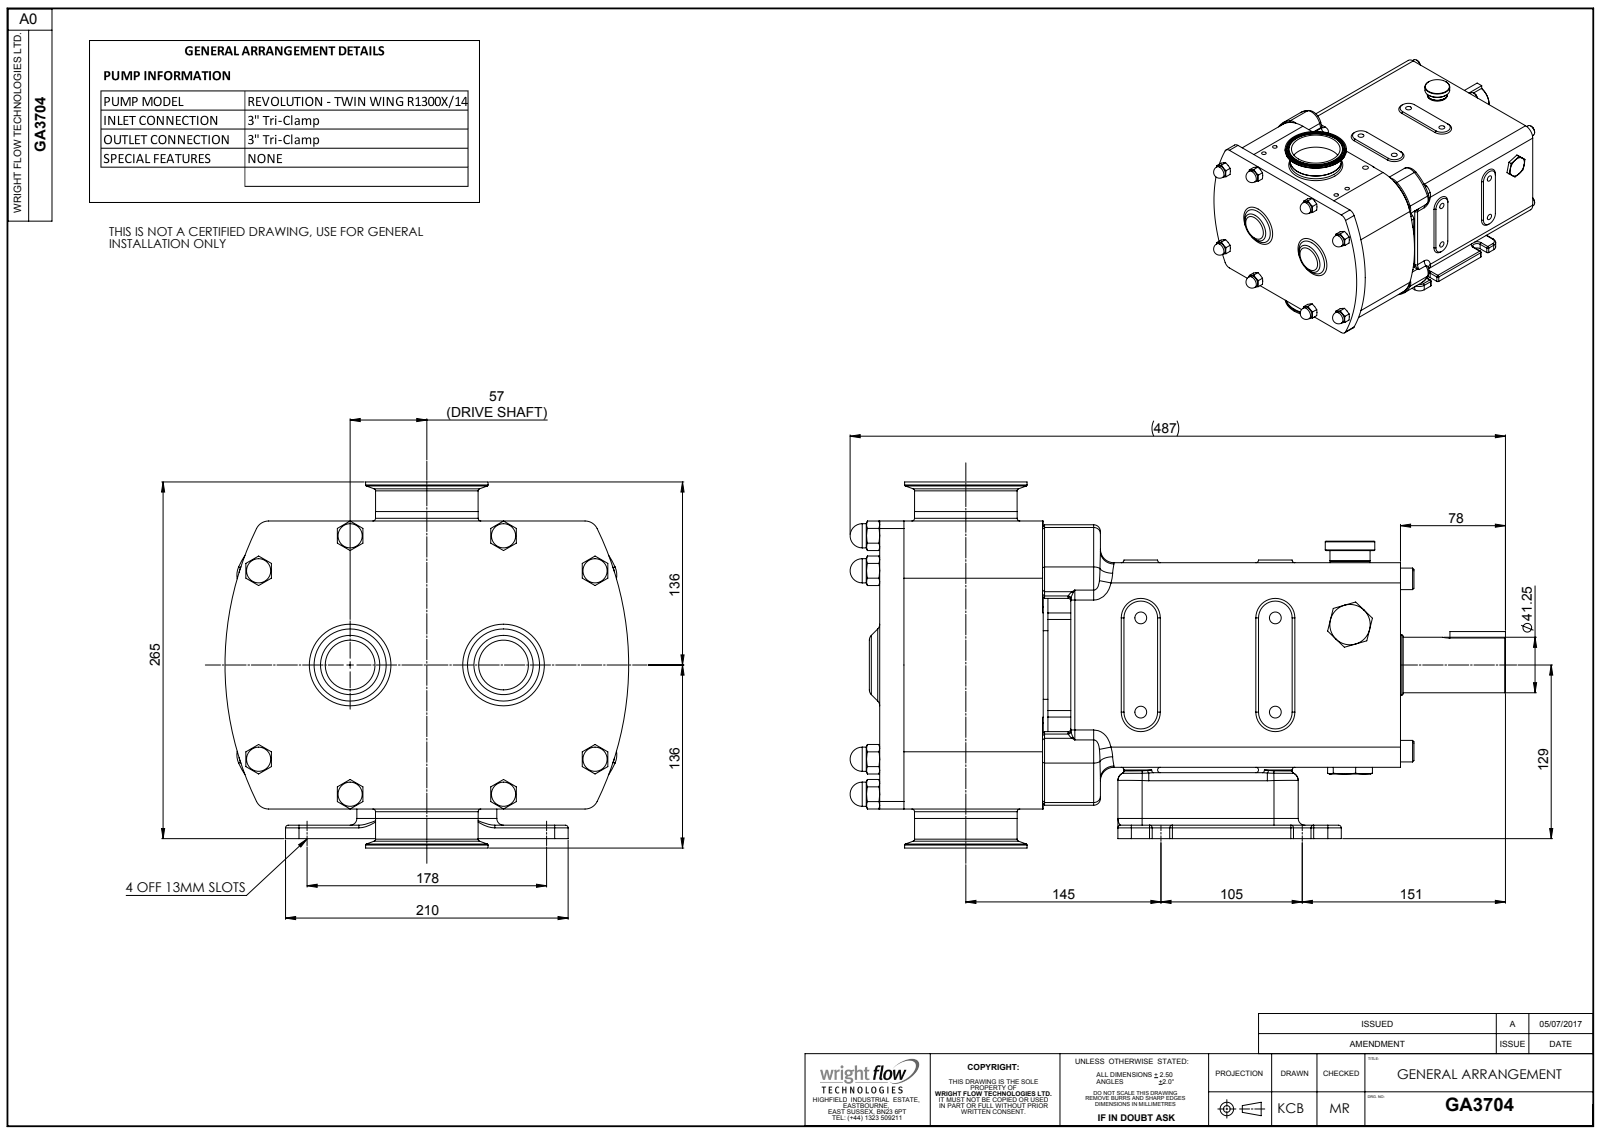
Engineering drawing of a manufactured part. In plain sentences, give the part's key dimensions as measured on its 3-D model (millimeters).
The part is named "Copy of RA94-5121-55M^GA3704; Copy of R1300 CPP V LHD^GA3704; GA3704". Its 3-D file was written by "SolidWorks 2023 (AUTOMOTIVE_DESIGN)". It is 3 solids with 937 faces: 290 planar, 277 cylindrical and 370 other. Overall it measures 487 by 300 by 272 millimeters. Its volume is 18 670 000 cubic millimeters and its surface area 708 203 square millimeters. Round holes: 8 of diameter 8.8, 4 of diameter 6.8, 2 of diameter 8.6, 1 of diameter 33.8, 1 of diameter 72.25. Round bosses or shafts: 8 of diameter 18, 6 of diameter 16, 1 of diameter 91, 1 of diameter 76.3, 1 of diameter 76.2, 1 of diameter 51, 1 of diameter 45, 1 of diameter 41.25. Partial cylindrical surfaces (rounded edges, fillets, slot ends): 38 of radius 2, 30 of radius 10, 19 of radius 5, 8 of radius 5.9, 8 of radius 15, 8 of radius 18, 4 of radius 3, 4 of radius 6. The main face-to-face distances are 152, 121.5, 265.5, 387, 31, 183, 125, 3.5, 262, 43. The hole center spacings are 70, 100, 122.07, 23, 60.56, 74.2, 76.66, 82.71.
